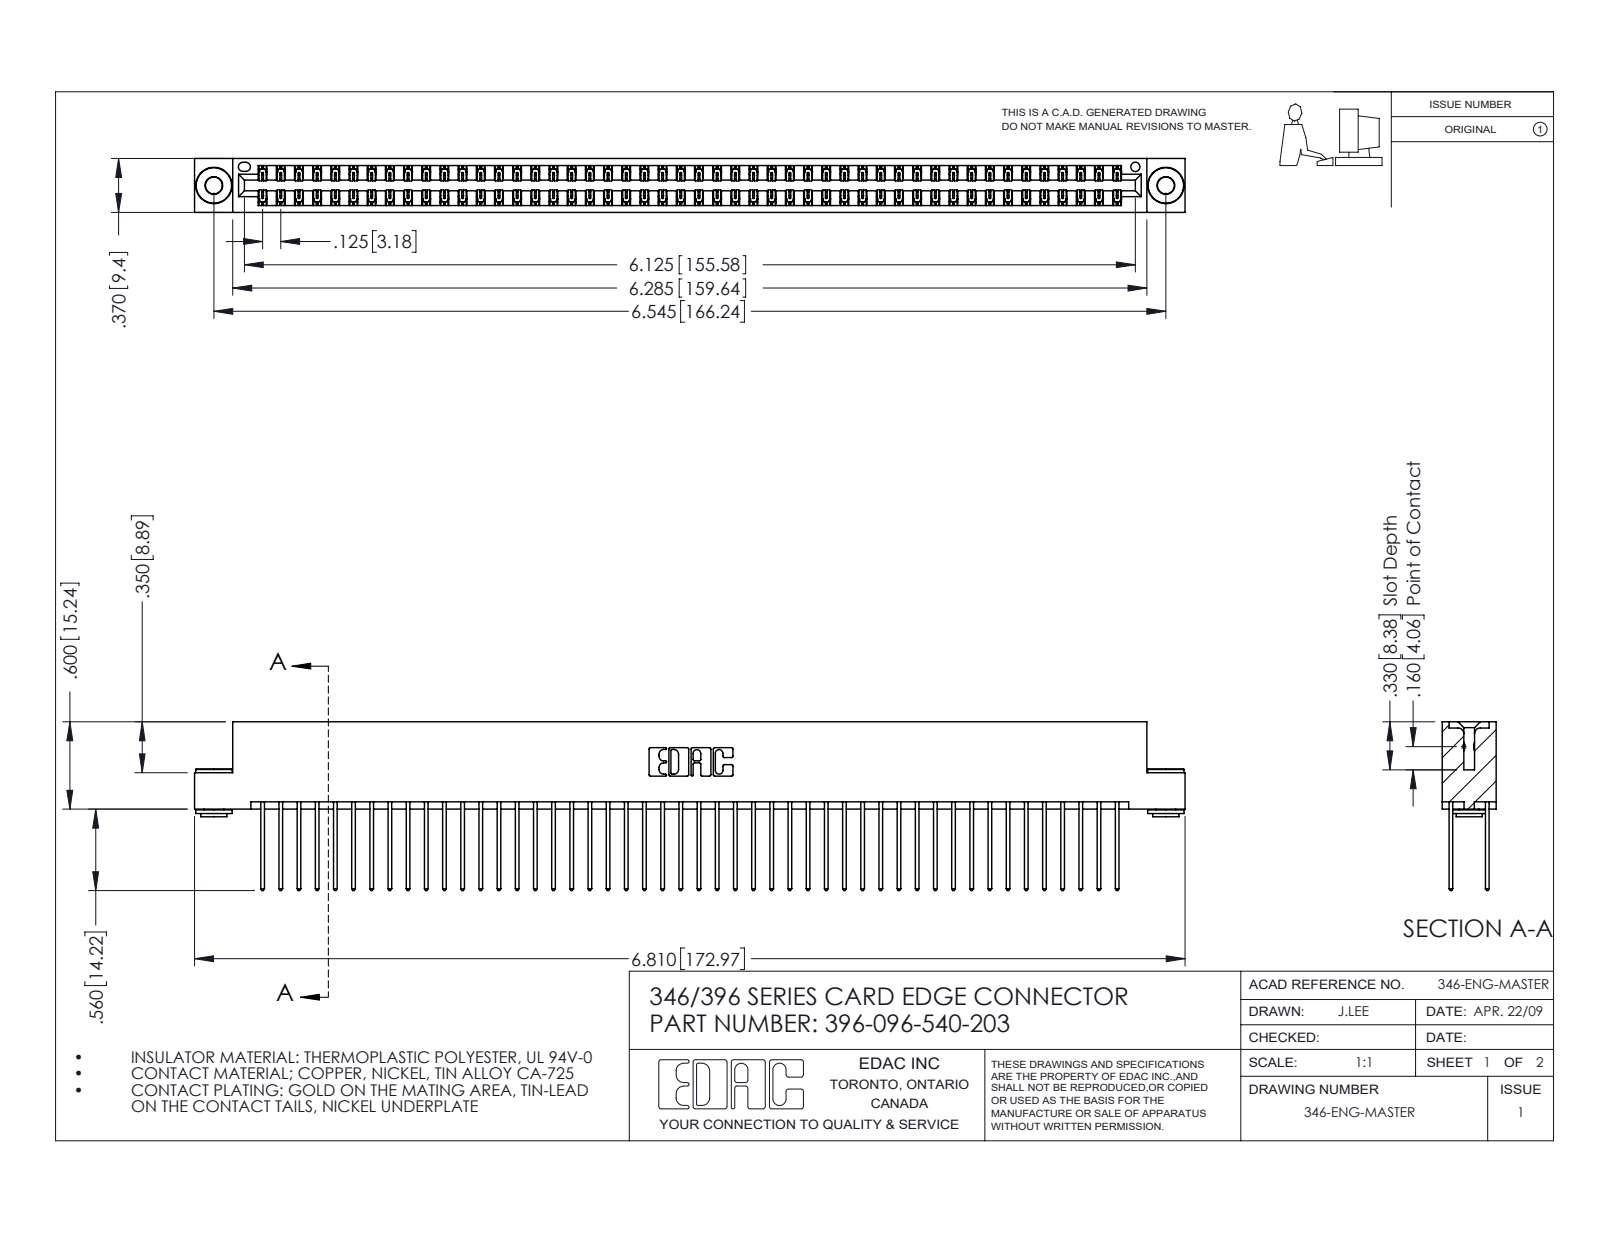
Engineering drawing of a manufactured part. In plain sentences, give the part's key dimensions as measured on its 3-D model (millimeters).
The part is named "345-250-002_345-250-002-102; 345-292-001_345-293-140; 346 Part_Flush Mounting Lugs - 0.156 Dia-TH; 396-096-540-203". Its 3-D file was written by "SolidWorks 2016 (CONFIG_CONTROL_DESIGN)". It is 99 solids with 5152 faces: 3446 planar, 1698 cylindrical and 8 other. Overall it measures 173 by 29.5 by 9.4 millimeters. Its volume is 17 300 cubic millimeters and its surface area 25 810 square millimeters. Round holes: 2 of diameter 2.9, 2 of diameter 4, 1 of diameter 1.6. Round bosses or shafts: 2 of diameter 6.4, 2 of diameter 4.6, 2 of diameter 3.5. Partial cylindrical surfaces (rounded edges, fillets, slot ends): 144 of radius 0.2, 96 of radius 0.3, 22 of radius 0.3, 6 of radius 0.2, 6 of radius 0.8, 3 of radius 0.7, 2 of radius 0.4, 2 of radius 0.6. The main face-to-face distances are 1.2, 8.2, 6.4, 0.6, 1.8, 7.6, 9.4, 7, 3.8, 5.6. The hole center spacings are 6.2, 160.9, 166.2.
